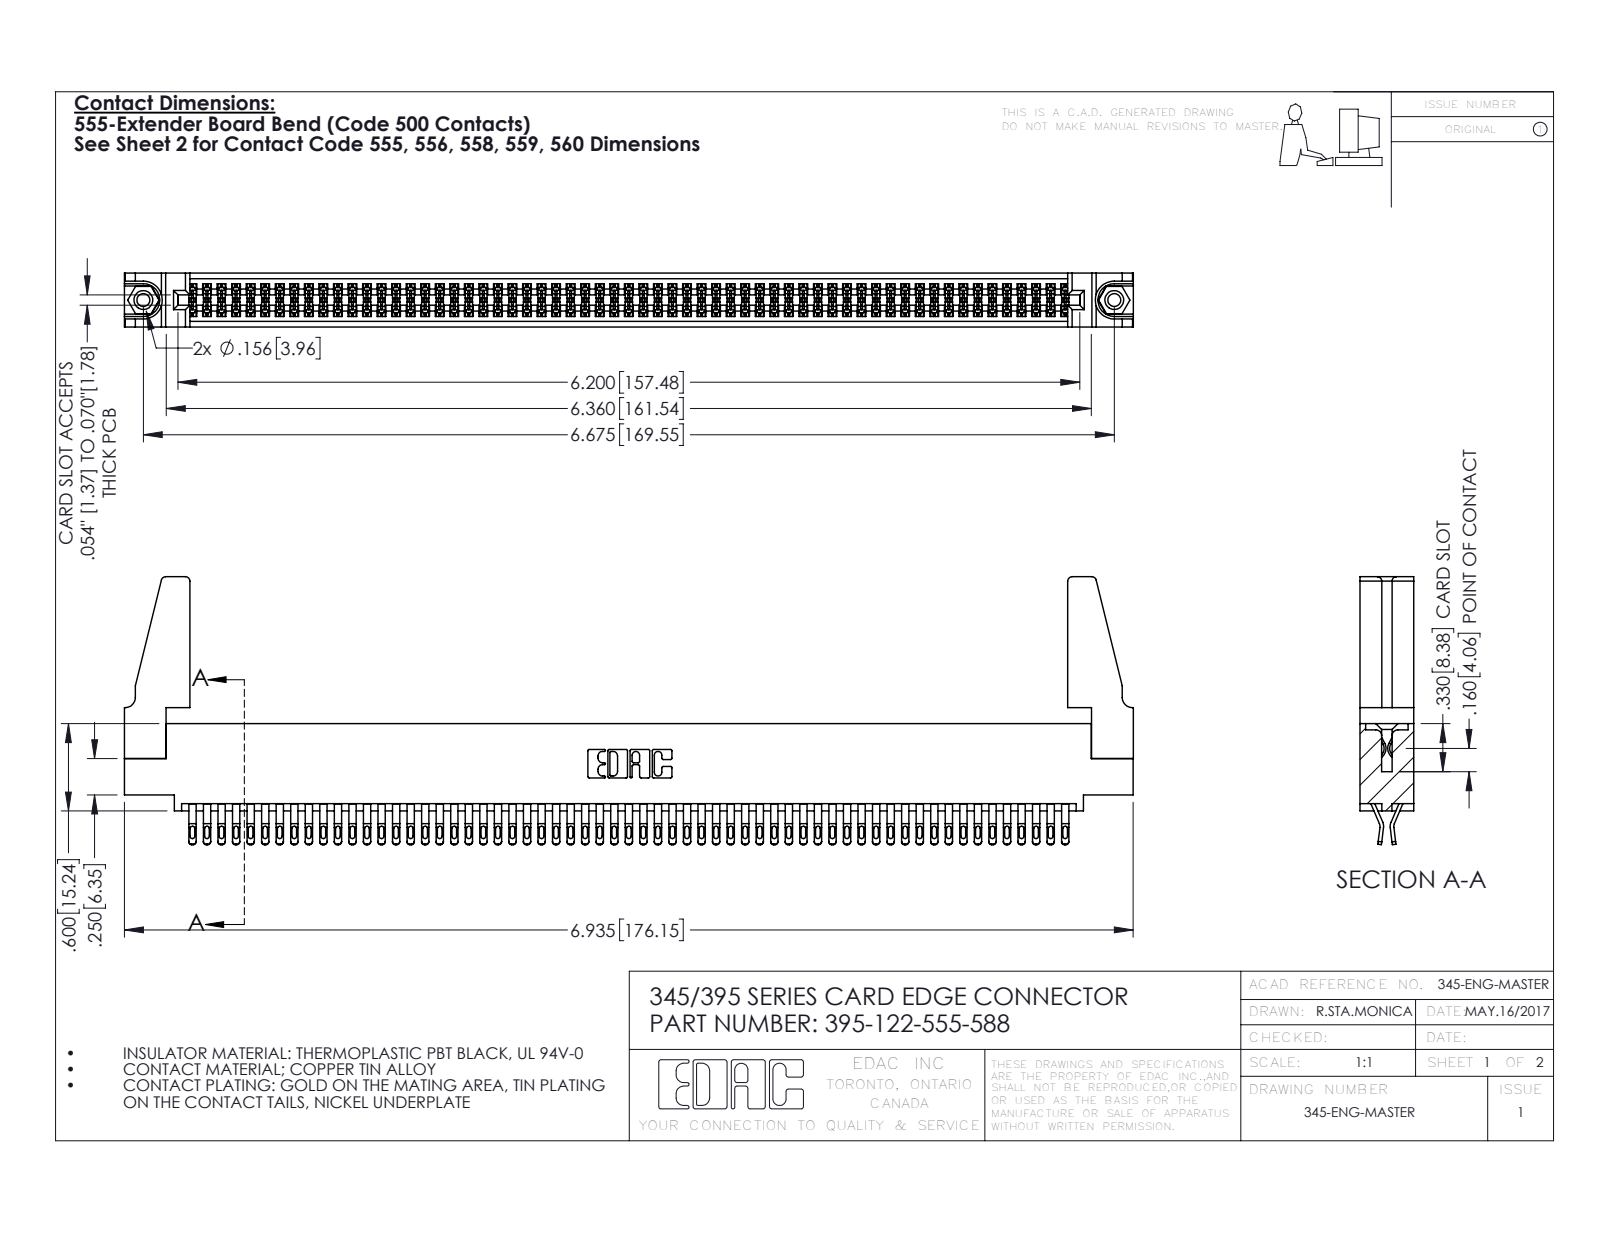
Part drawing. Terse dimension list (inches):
name: 345-292-001_555 Tail; 345-250-001_345-250-001-102; 395-122-555-588; 345 Part_0.110 Offset - 0.156 Dia-TH (+1 more)
written by: SolidWorks 2016 (CONFIG_CONTROL_DESIGN)
unit: in
bodies: 127 solids, 7086 faces (3938 planar, 3132 cylindrical, 16 other)
size: 6.936 × 1.842 × 0.37
volume: 1.271 in³; area: 47.72 in²
holes: 2× ⌀0.089, 2× ⌀0.125, 2× ⌀0.156, 1× ⌀0.064
bosses: 2× ⌀0.155
rounds: 305× R0.016, 244× R0.02, 183× R0.006, 22× R0.01, 8× R0.03, 6× R0.007, 6× R0.031, 3× R0.026
face distances: 0.072, 0.298, 0.37, 0.025, 0.2, 0.098, 0.272, 0.225, 0.175, 0.149
hole spacings: 0.27, 6.439, 6.675
